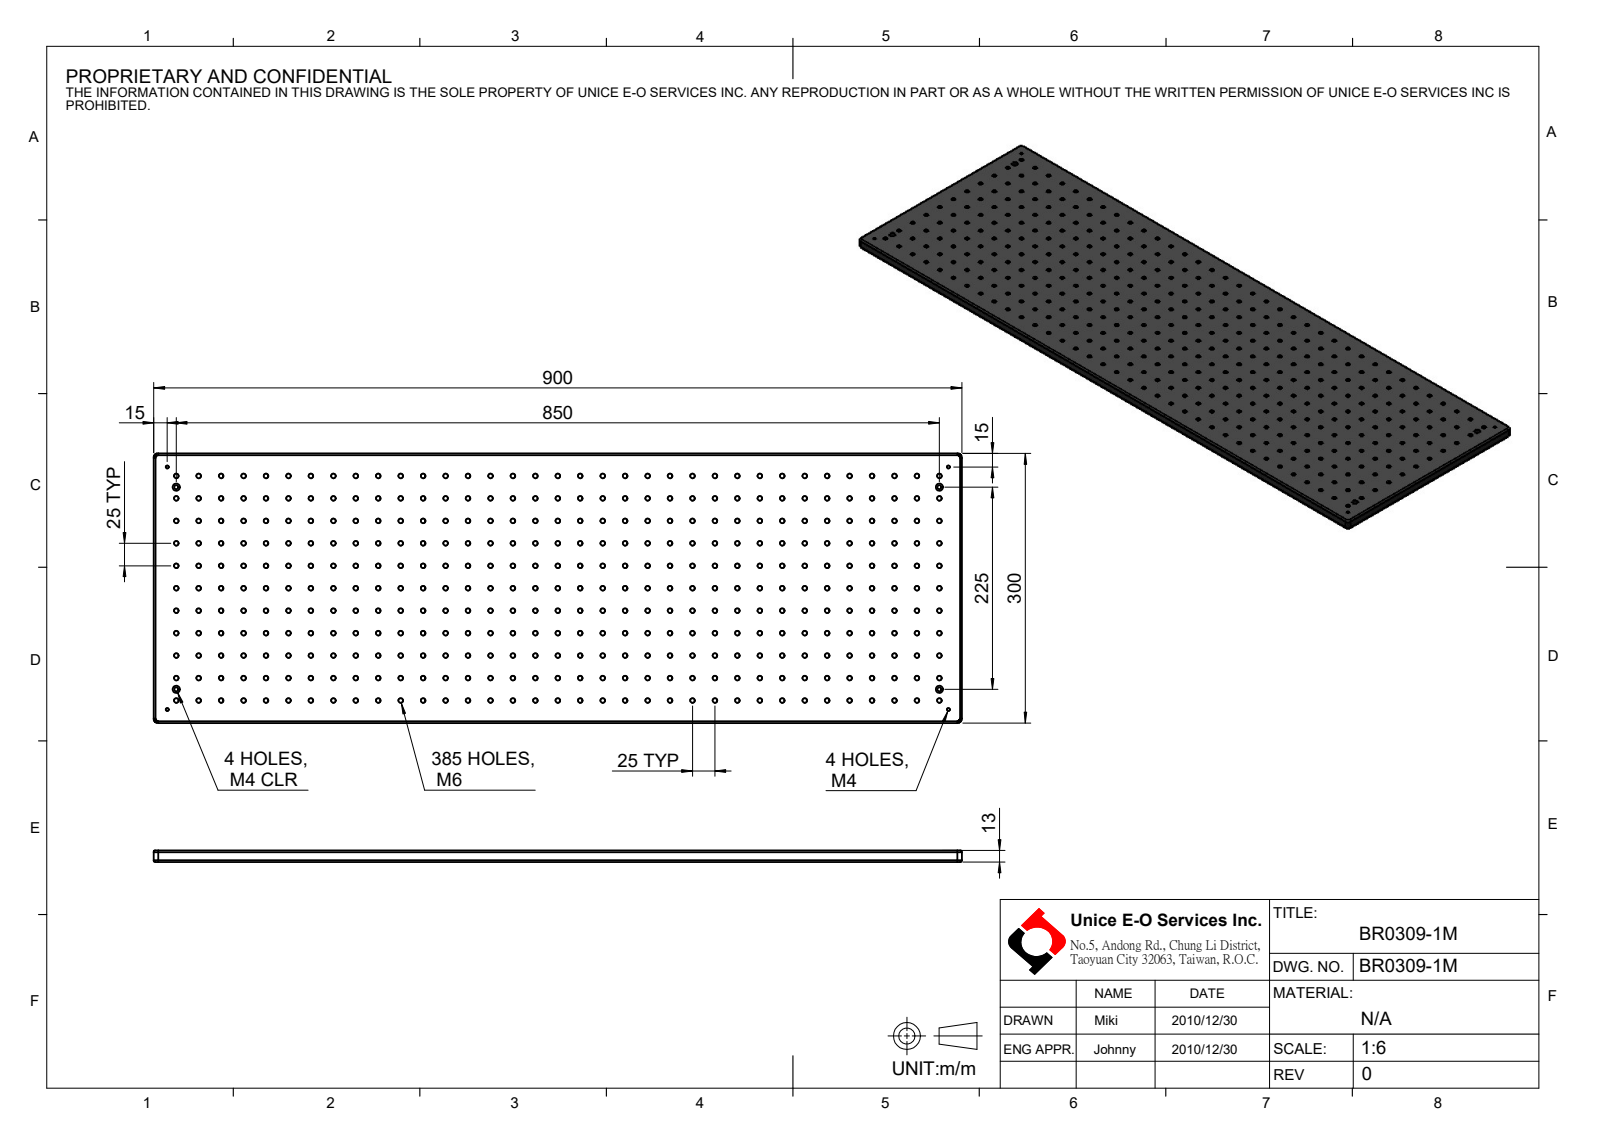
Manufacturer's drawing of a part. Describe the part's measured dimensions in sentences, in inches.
The part is named "BR0309-1M". Its 3-D file was written by "SolidWorks 2016 (CONFIG_CONTROL_DESIGN)". It is 1 solid with 824 faces: 10 planar, 806 cylindrical and 8 other. Overall it measures 35.433 by 11.811 by 0.512 inches. Its volume is 207.8 cubic inches and its surface area 979.3 square inches. Round holes: 385 of diameter 0.197, 4 of diameter 0.13, 4 of diameter 0.177, 4 of diameter 0.315. Partial cylindrical surfaces (rounded edges, fillets, slot ends): 8 of radius 0.079, 4 of radius 0.197. The main face-to-face distances are 0.512, 11.811, 35.433, 0.276, 0.236. The hole center spacings are 0.984, 1.969, 2.953, 3.937, 4.921, 5.906, 6.89, 8.858.
